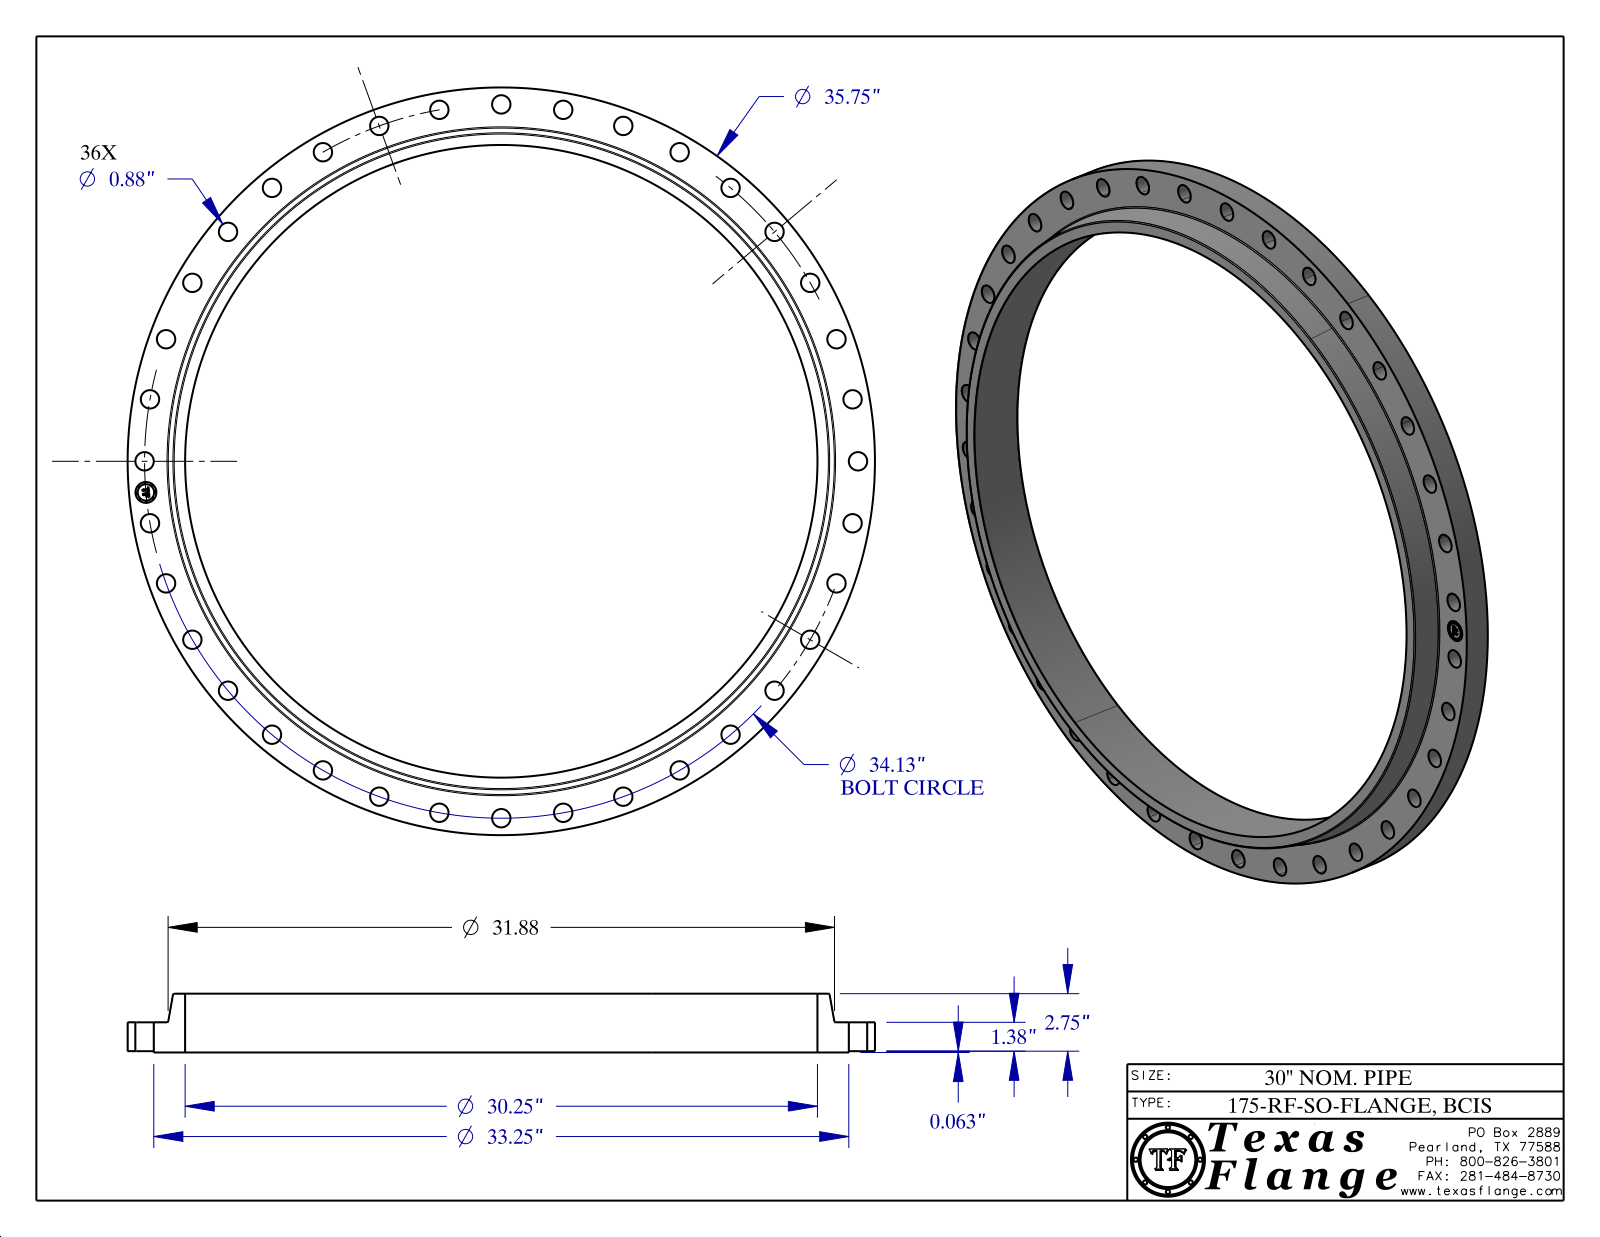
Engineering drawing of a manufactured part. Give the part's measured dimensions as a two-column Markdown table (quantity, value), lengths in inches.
| quantity | value |
| --- | --- |
| part name | 175-RF-SO |
| STEP written by | CATIA V5 STEP AP214 (AUTOMOTIVE_DESIGN) |
| units | inches |
| bodies | 1 solid, 473 faces (369 planar, 98 cylindrical, 6 other) |
| overall size | 35.75 × 35.75 × 2.813 |
| volume | 465 in³ |
| surface area | 1 204 in² |
| round holes (diameter × count) | 0.88 × 36, 1 × 1, 30.25 × 1 |
| round bosses / shafts (diameter × count) | 0.061 × 8, 35.75 × 1, 33.25 × 1, 0.788 × 1 |
| main face-to-face distances | 1.443, 0.063, 1.38, 2.813, 2.75, 1.37, 1.428, 1.365, 0.015, 1.385 |
| hole center spacings | 17.065, 29.557, 2.975, 5.927, 26.145, 34, 8.833, 21.939 |
